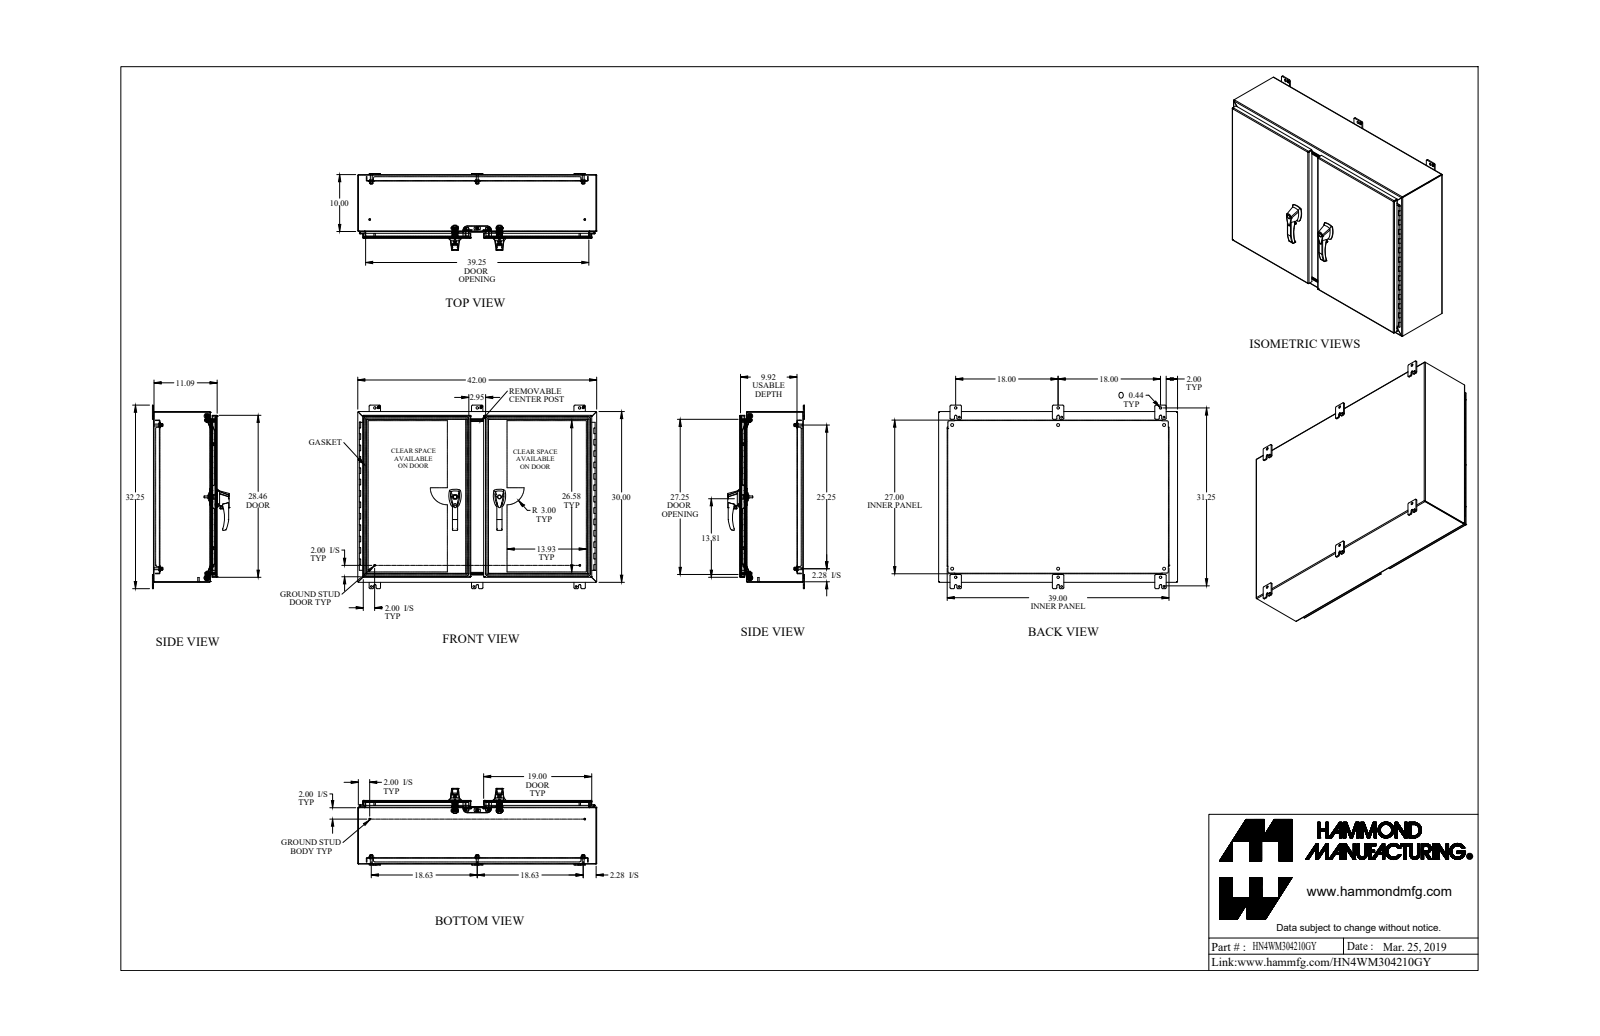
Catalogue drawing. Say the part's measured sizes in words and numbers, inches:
The part is named "HN4WM304210GY". Its 3-D file was written by "SolidWorks 2018 (AUTOMOTIVE_DESIGN)". It is 102 solids with 2784 faces: 1305 planar, 1187 cylindrical and 292 other. Overall it measures 42 by 32.25 by 13.487 inches. Its volume is 604.6 cubic inches and its surface area 12 427 square inches. Round holes: 10 of diameter 0.304, 9 of diameter 0.313, 8 of diameter 0.25, 6 of diameter 0.201, 6 of diameter 0.307, 6 of diameter 0.445, 6 of diameter 0.5, 4 of diameter 0.281, 4 of diameter 0.313, 4 of diameter 0.39, 3 of diameter 0.437, 2 of diameter 0.11. Round bosses or shafts: 8 of diameter 1, 8 of diameter 0.281, 6 of diameter 0.65, 6 of diameter 0.375, 6 of diameter 0.33, 6 of diameter 0.293, 4 of diameter 0.75, 4 of diameter 0.625. Partial cylindrical surfaces (rounded edges, fillets, slot ends): 37 of radius 0.125, 34 of radius 0.25, 32 of radius 0.018, 28 of radius 0.188, 22 of radius 0.06, 22 of radius 0.5, 19 of radius 0.048, 19 of radius 0.143. The main face-to-face distances are 0.095, 1.032, 0.095, 11.09, 10.995, 0.937, 11.185, 11.09, 9.963, 1.127. The hole center spacings are 31.376, 6, 40.588, 18.625, 12, 25.25, 37.25, 41.897.
